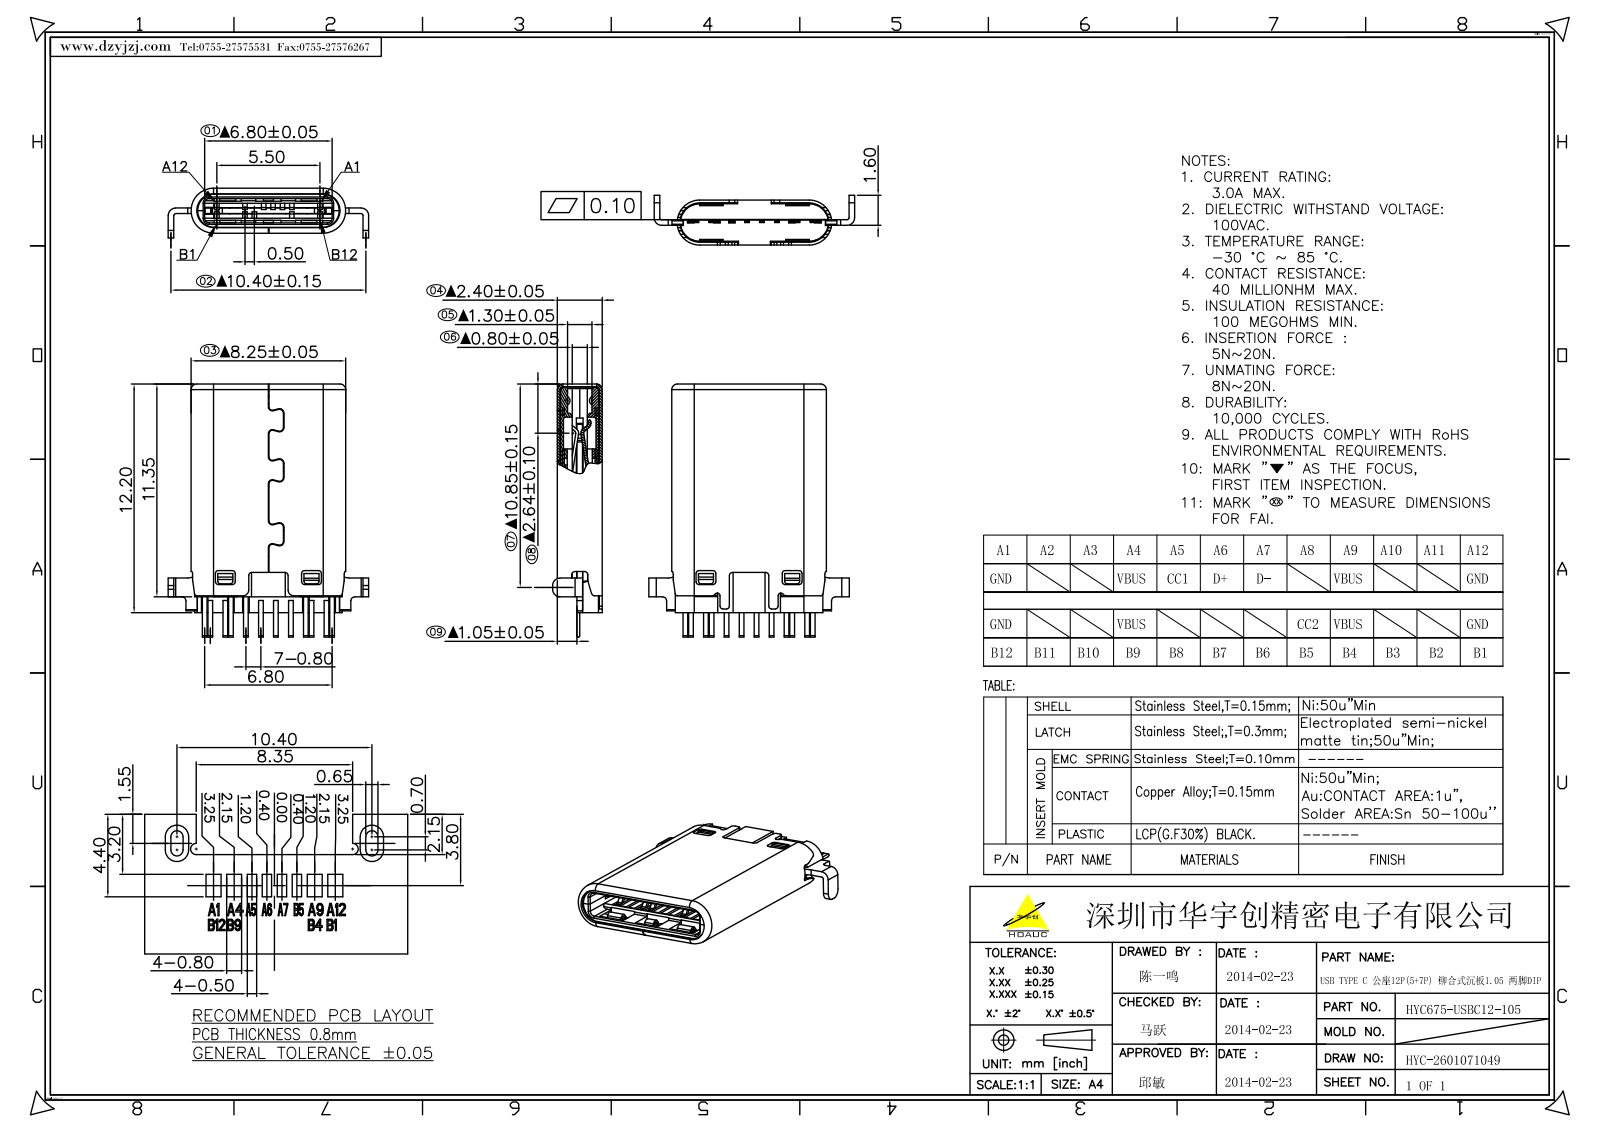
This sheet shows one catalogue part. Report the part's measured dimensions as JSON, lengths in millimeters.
{"part_name": "TANPIAN-PLASTIC_1_2__2_1_11_1_1", "step_written_by": "CREO PARAMETRIC BY PTC INC, 2022073 (AUTOMOTIVE_DESIGN)", "units": "millimeters", "bodies": {"solids": 1, "faces": 595, "planar": 429, "cylindrical": 162, "other": 4}, "overall_size": [13.5, 10.7, 2.65], "volume_mm3": 183, "surface_area_mm2": 499, "partial_cylinders_radius": [[0.15, 26], [0.2, 14], [0.25, 10], [0.3, 10], [0.17, 6], [0.23, 6], [0.1, 4], [0.13, 4]], "face_to_face_distances": [0.8, 2.4, 1.05, 1.6, 0.55, 0.5, 1.35, 1.04, 0.9, 0.4]}
